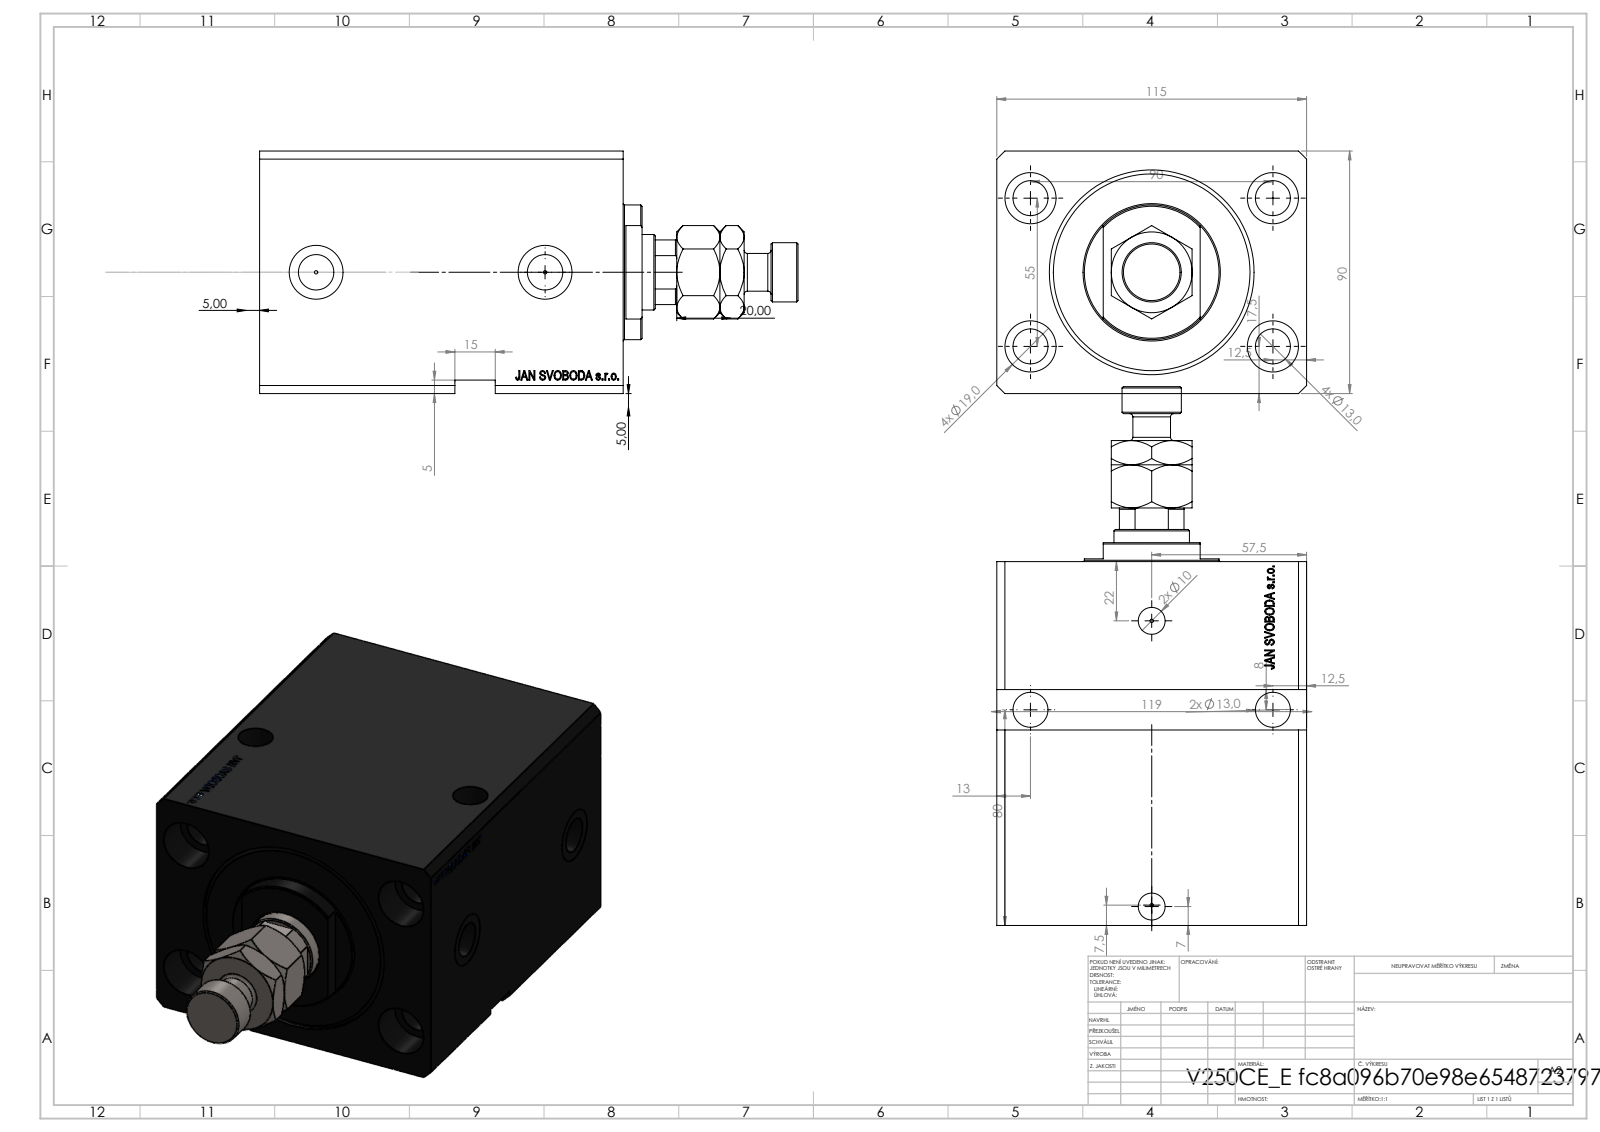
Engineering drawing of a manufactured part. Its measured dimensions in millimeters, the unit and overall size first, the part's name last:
Units: millimetres
Overall size (bounding box): 200 × 115 × 90
Round holes (diameter × count): ⌀13 ×8, ⌀1.25 ×4, ⌀19 ×4, ⌀10 ×2, ⌀13.16 ×2, ⌀20 ×2, ⌀18.5 ×1, ⌀28 ×1, ⌀63 ×1, ⌀76 ×1
Round bosses / shafts (diameter × count): ⌀50 ×1, ⌀22 ×1, ⌀14 ×1
Partial cylindrical surfaces — rounded edges, fillets, slot ends (radius × count): R13.5 ×1
Main face-to-face distances: 115, 90, 20, 135, 17.9, 117.1, 97.1, 65, 13, 47.1
Hole centre spacings: 52.74, 55.8, 85.76, 90, 40, 55, 55.49, 85.3
Volume: 1 165 000 mm³ · Surface area: 180 657 mm²
Bodies: 4 solids, 1025 faces (487 planar, 120 cylindrical, 418 other)
Part name (STEP PRODUCT): V250CE_VC_E; V250CE_E_Body; MFA; V250CE_C_VCP
STEP written by: SolidWorks 2019 (CONFIG_CONTROL_DESIGN)
